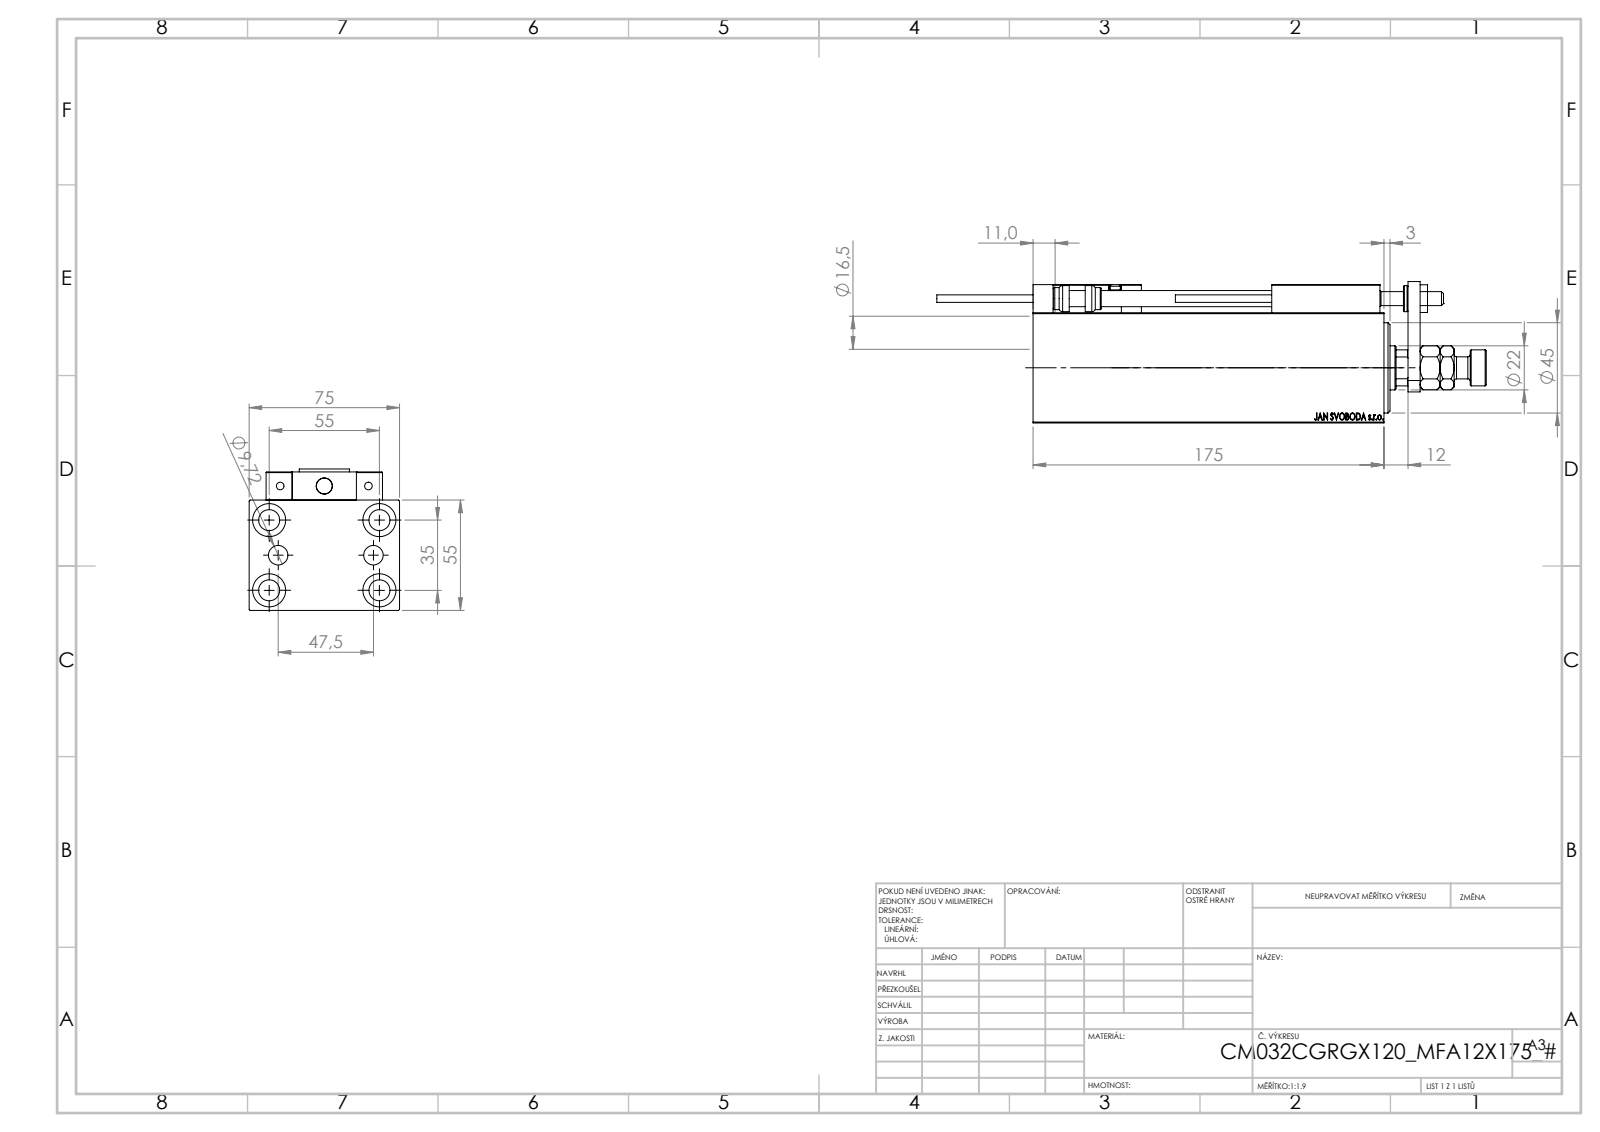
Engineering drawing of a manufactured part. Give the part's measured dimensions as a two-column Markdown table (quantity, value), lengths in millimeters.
| quantity | value |
| --- | --- |
| part name | Block; ALLEN BOLT D5; V450CM_C_Body; SWITCH X (+7 more) |
| STEP written by | SolidWorks 2019 (CONFIG_CONTROL_DESIGN) |
| units | millimeters |
| bodies | 24 solids, 1330 faces (576 planar, 188 cylindrical, 566 other) |
| overall size | 274 × 75 × 70.5 |
| volume | 659 986 mm³ |
| surface area | 151 033 mm² |
| round holes (diameter × count) | 4 × 6, 8 × 5, 10.5 × 5, 16.5 × 5, 3.2 × 4, 5 × 2, 9.72 × 2, 7 × 1, 22 × 1, 25.5 × 1, 32 × 1, 34 × 1 |
| round bosses / shafts (diameter × count) | 11 × 2, 5 × 2, 3.8 × 2, 18 × 1, 13 × 1 |
| partial cylindrical surfaces (radius × count) | 0.3 × 30, 3 × 2, 10.5 × 1 |
| main face-to-face distances | 55, 75, 14, 10, 3, 69, 23, 18, 25, 12 |
| hole center spacings | 17.9, 32.6, 54.16, 11.37, 20, 23.75, 29.59, 29.69 |
